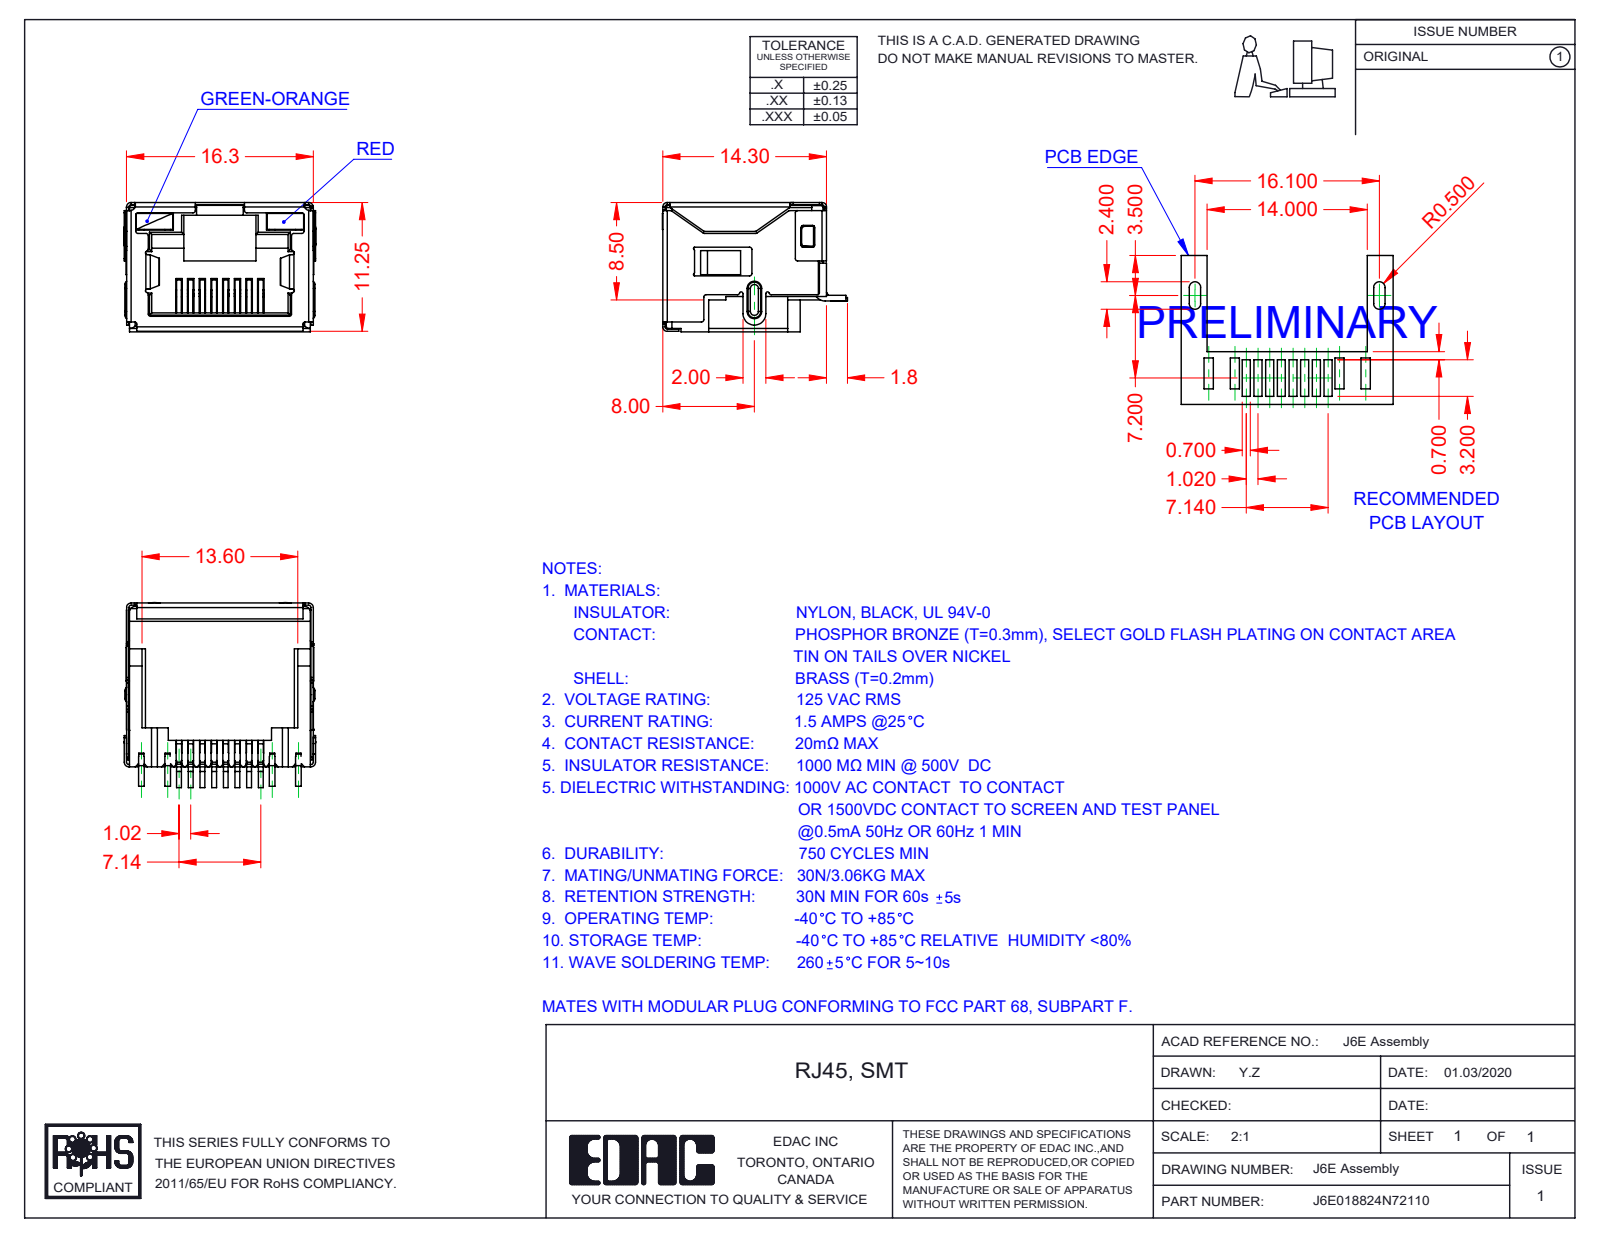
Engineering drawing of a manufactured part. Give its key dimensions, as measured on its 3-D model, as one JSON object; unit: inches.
{"part_name": "6E Shield_LED; 6E LED RH_2-Red; J6E018824N72110; 6E LED LH_7-Green-Orange (+2 more)", "step_written_by": "SolidWorks 2016 (CONFIG_CONTROL_DESIGN)", "units": "inches", "bodies": {"solids": 12, "faces": 1498, "planar": 1099, "cylindrical": 349, "other": 50}, "overall_size": [0.659, 0.636, 0.445], "volume_in3": 0.068, "surface_area_in2": 6.27, "partial_cylinders_radius": [[0.008, 82], [0.01, 17], [0.016, 13], [0.02, 13], [0.004, 10], [0.006, 7], [0.012, 4], [0.039, 3]], "face_to_face_distances": [0.435, 0.632, 0.634, 0.624, 0.437, 0.445, 0.094, 0.028, 0.388, 0.019]}
